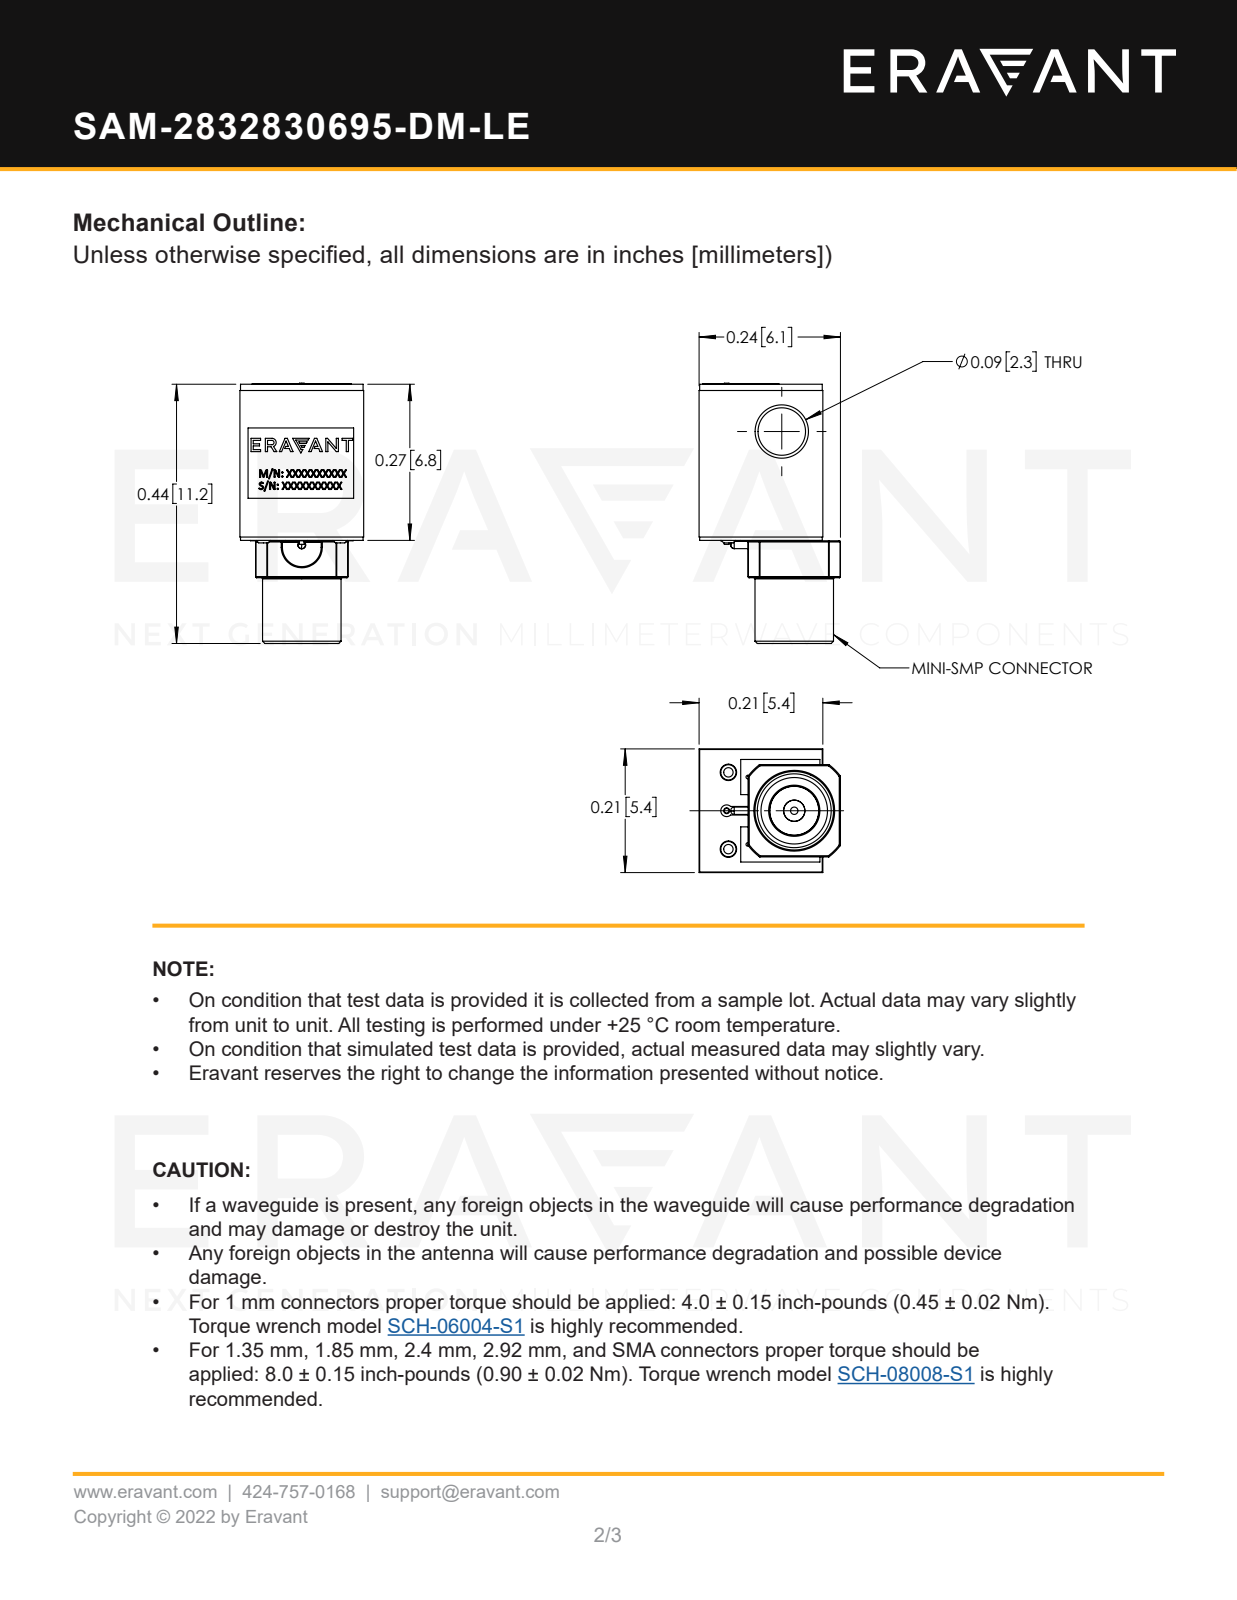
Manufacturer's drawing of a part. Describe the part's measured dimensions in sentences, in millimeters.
The part is named "AM-CA-9550-EL". Its 3-D file was written by "SolidWorks 2021 (CONFIG_CONTROL_DESIGN)". It is 1 solid with 162 faces: 53 planar, 53 cylindrical and 56 other. Overall it measures 11.28 by 6.12 by 5.36 millimeters. Its volume is 218 cubic millimeters and its surface area 315 square millimeters. Round holes: 2 of diameter 0.71, 1 of diameter 0.25, 1 of diameter 2.06, 1 of diameter 2.14, 1 of diameter 2.22, 1 of diameter 2.88. Round bosses or shafts: 2 of diameter 0.66, 1 of diameter 3.4, 1 of diameter 0.32, 1 of diameter 0.2. Partial cylindrical surfaces (rounded edges, fillets, slot ends): 1 of radius 0.25, 1 of radius 0.7, 1 of radius 2.5. The main face-to-face distances are 5.36, 6.78, 6.76, 6.8, 0.68, 4.68, 4, 5.33, 8.4, 8.38. The hole center spacings are 1.73, 3.79, 2.93, 3.32.
